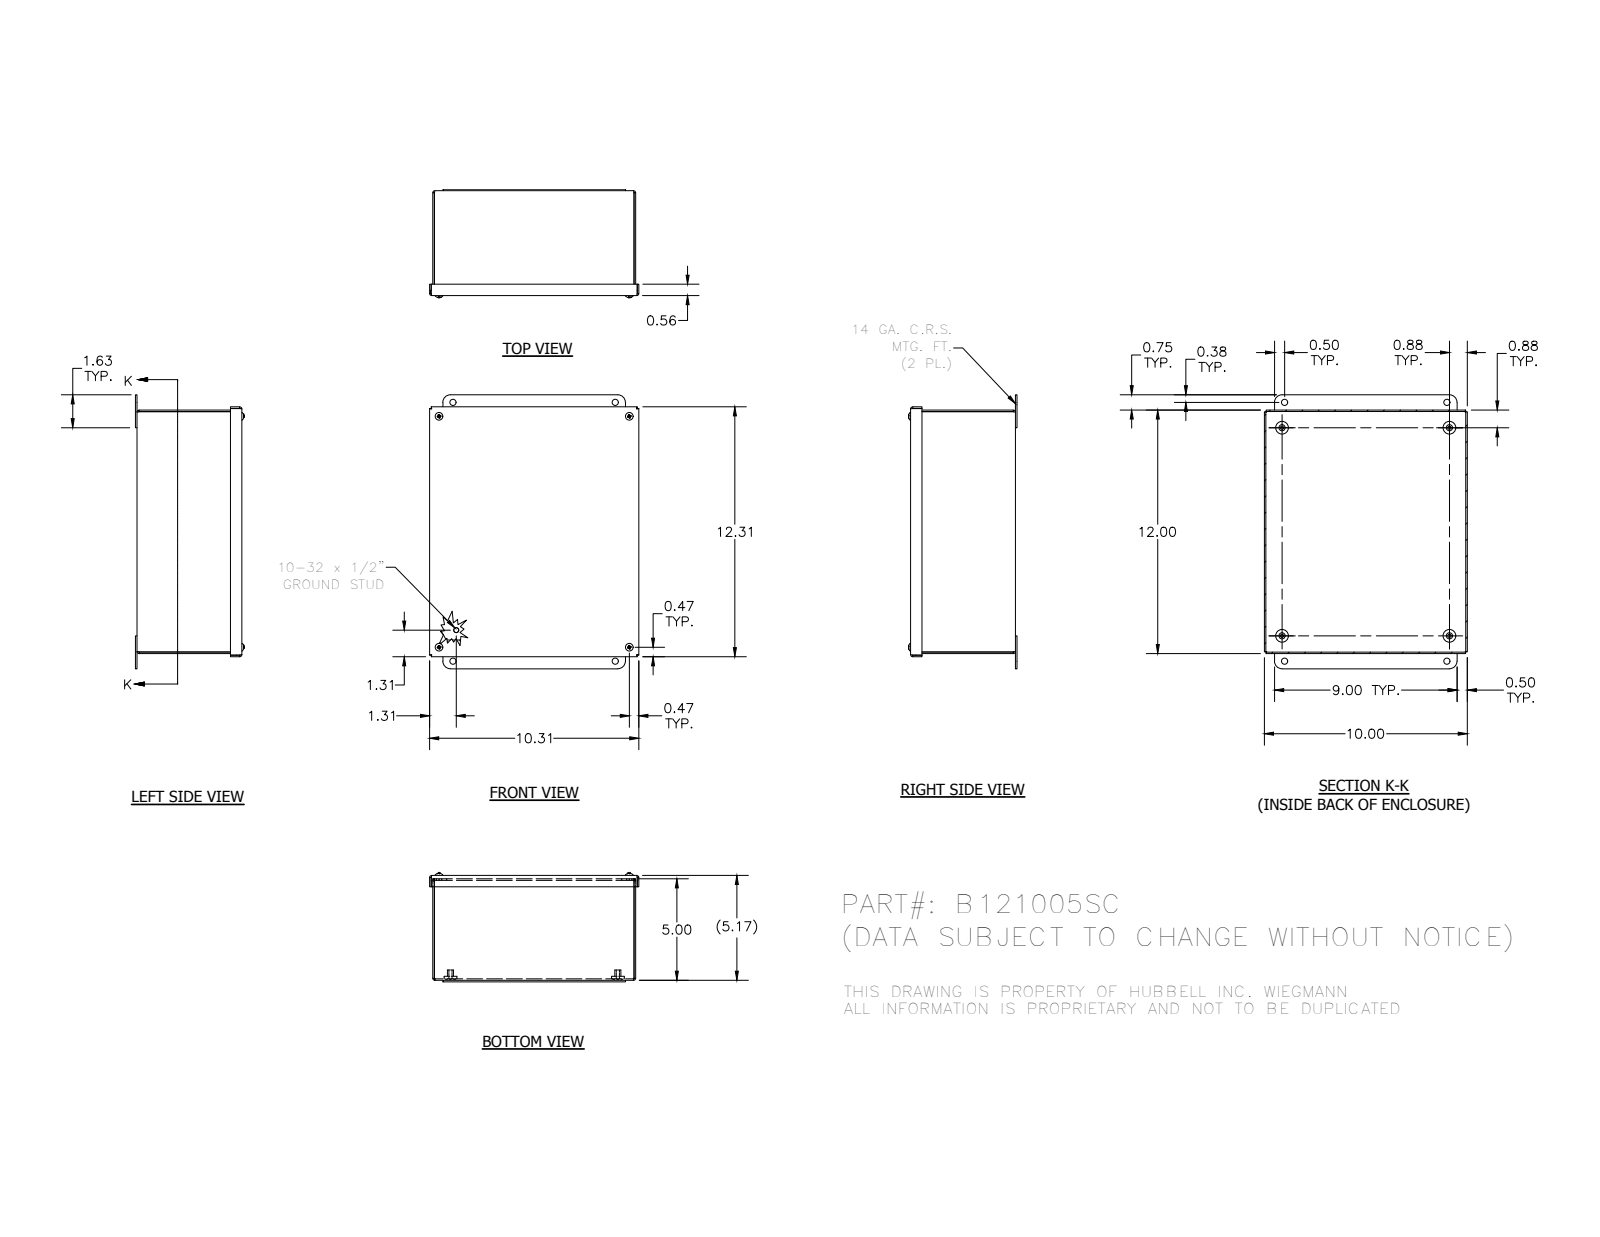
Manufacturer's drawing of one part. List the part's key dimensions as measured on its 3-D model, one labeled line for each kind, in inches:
Part name (STEP PRODUCT): B121005SC; 3484; 34984; B121005SCBKP (+6 more)
STEP written by: Autodesk Inventor 2012 (AUTOMOTIVE_DESIGN)
Units: inches
Bodies: 23 solids, 532 faces (311 planar, 102 cylindrical, 119 other)
Overall size (bounding box): 13.5 × 10.313 × 5.346
Volume: 44.56 in³ · Surface area: 1 142 in²
Round holes (diameter × count): ⌀0.145 ×4, ⌀0.156 ×4, ⌀0.196 ×4, ⌀0.278 ×4, ⌀0.281 ×4, ⌀0.31 ×4, ⌀0.313 ×4
Round bosses / shafts (diameter × count): ⌀0.19 ×5, ⌀0.625 ×4, ⌀0.453 ×4, ⌀0.406 ×4, ⌀0.373 ×4, ⌀0.3 ×4, ⌀0.248 ×4, ⌀0.25 ×1
Partial cylindrical surfaces — rounded edges, fillets, slot ends (radius × count): R0.031 ×12, R0.105 ×12, R0.089 ×4, R0.375 ×4
Main face-to-face distances: 0.074, 5.094, 5.168, 5.02, 9.926, 11.926, 9.852, 10, 11.852, 12
Hole centre spacings: 8.714, 11.395, 0.972, 12.082, 14.865, 0.795, 0.796, 1.256
